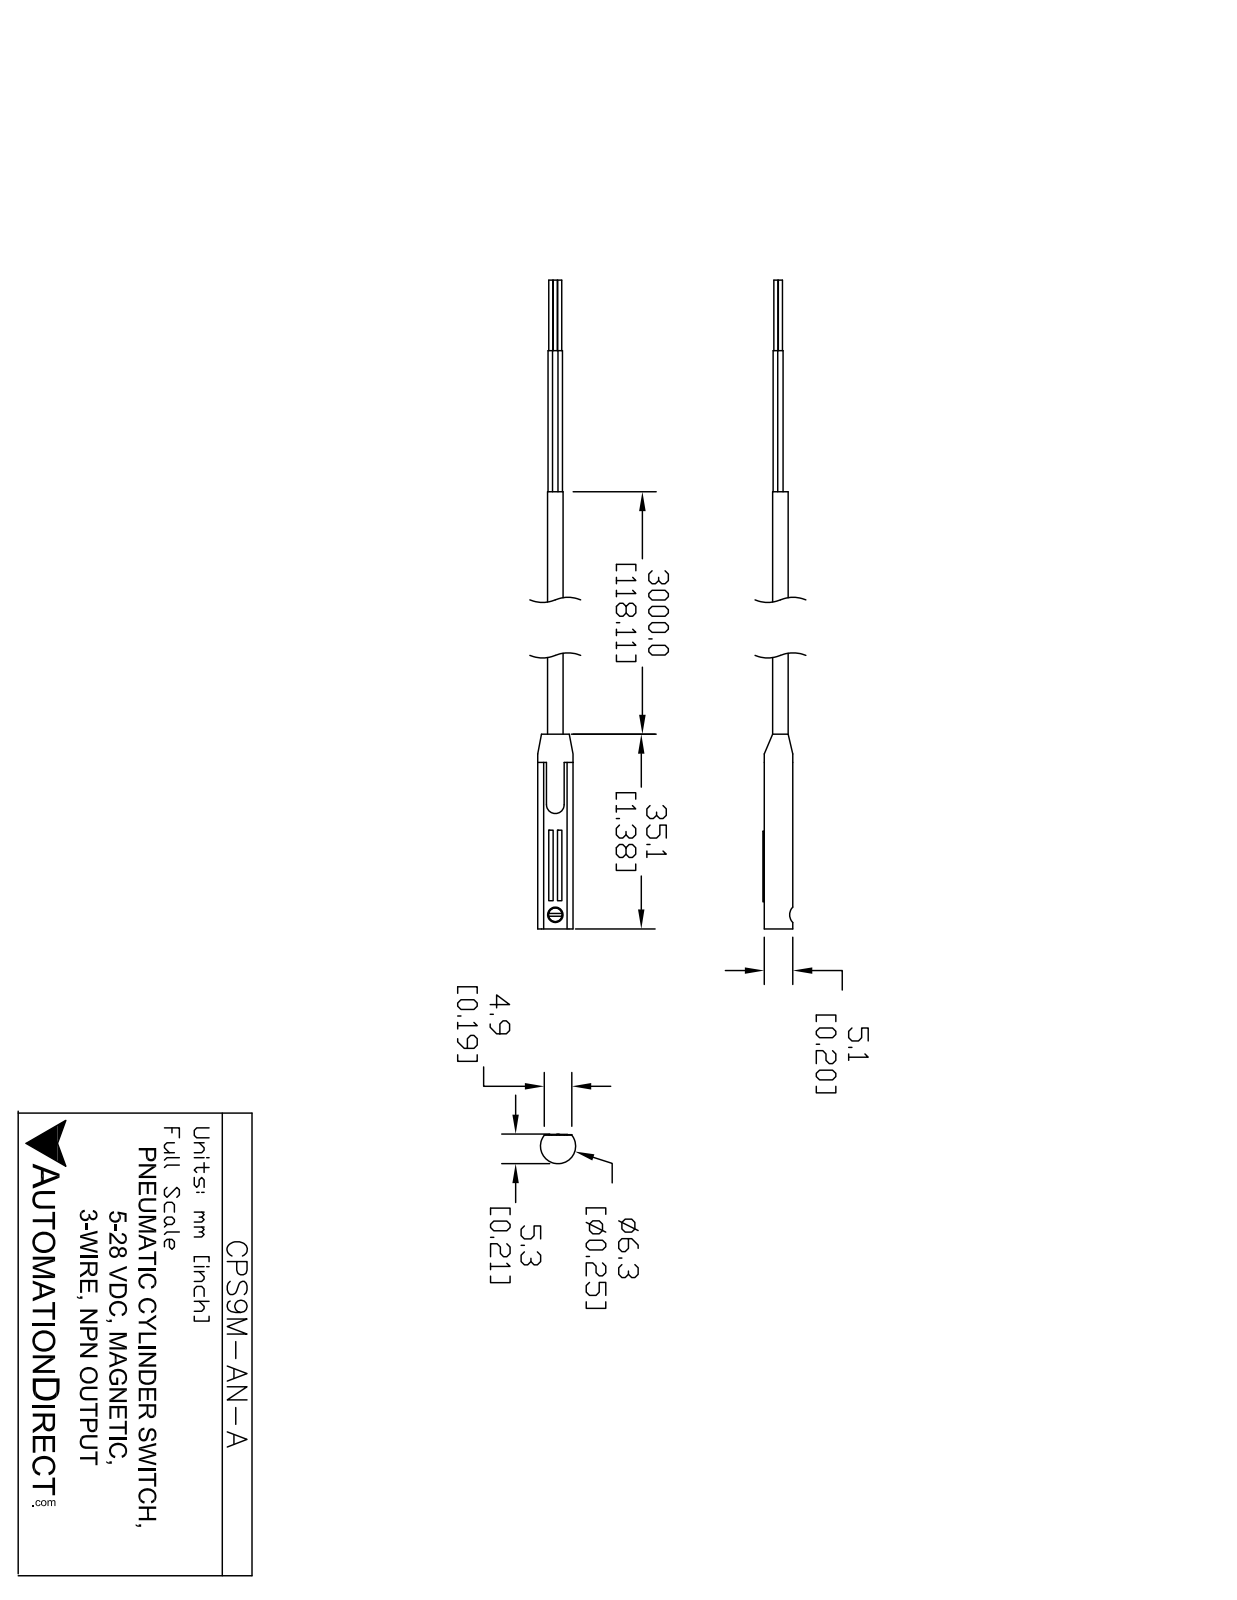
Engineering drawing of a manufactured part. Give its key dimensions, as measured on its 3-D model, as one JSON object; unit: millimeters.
{"part_name": "CPS9M-AN-A", "step_written_by": "SolidWorks 2017 (AUTOMOTIVE_DESIGN)", "units": "millimeters", "bodies": {"solids": 4, "faces": 122, "planar": 48, "cylindrical": 50, "other": 24}, "overall_size": [144.3, 6.4, 5.3], "volume_mm3": 1200, "surface_area_mm2": 2503, "round_holes": [[0.8, 1], [2.6, 1]], "round_bosses_or_shafts": [[3.5, 1], [2.7, 1]], "partial_cylinders_radius": [[0.1, 13], [0.4, 3], [0.8, 2], [1.1, 1], [1.6, 1], [2.7, 1], [3.2, 1]], "face_to_face_distances": [4.3, 0.5, 0.5, 3.7, 1.6, 1.1, 0.7, 1.8, 2.3, 30], "hole_center_spacings": [3.5]}
